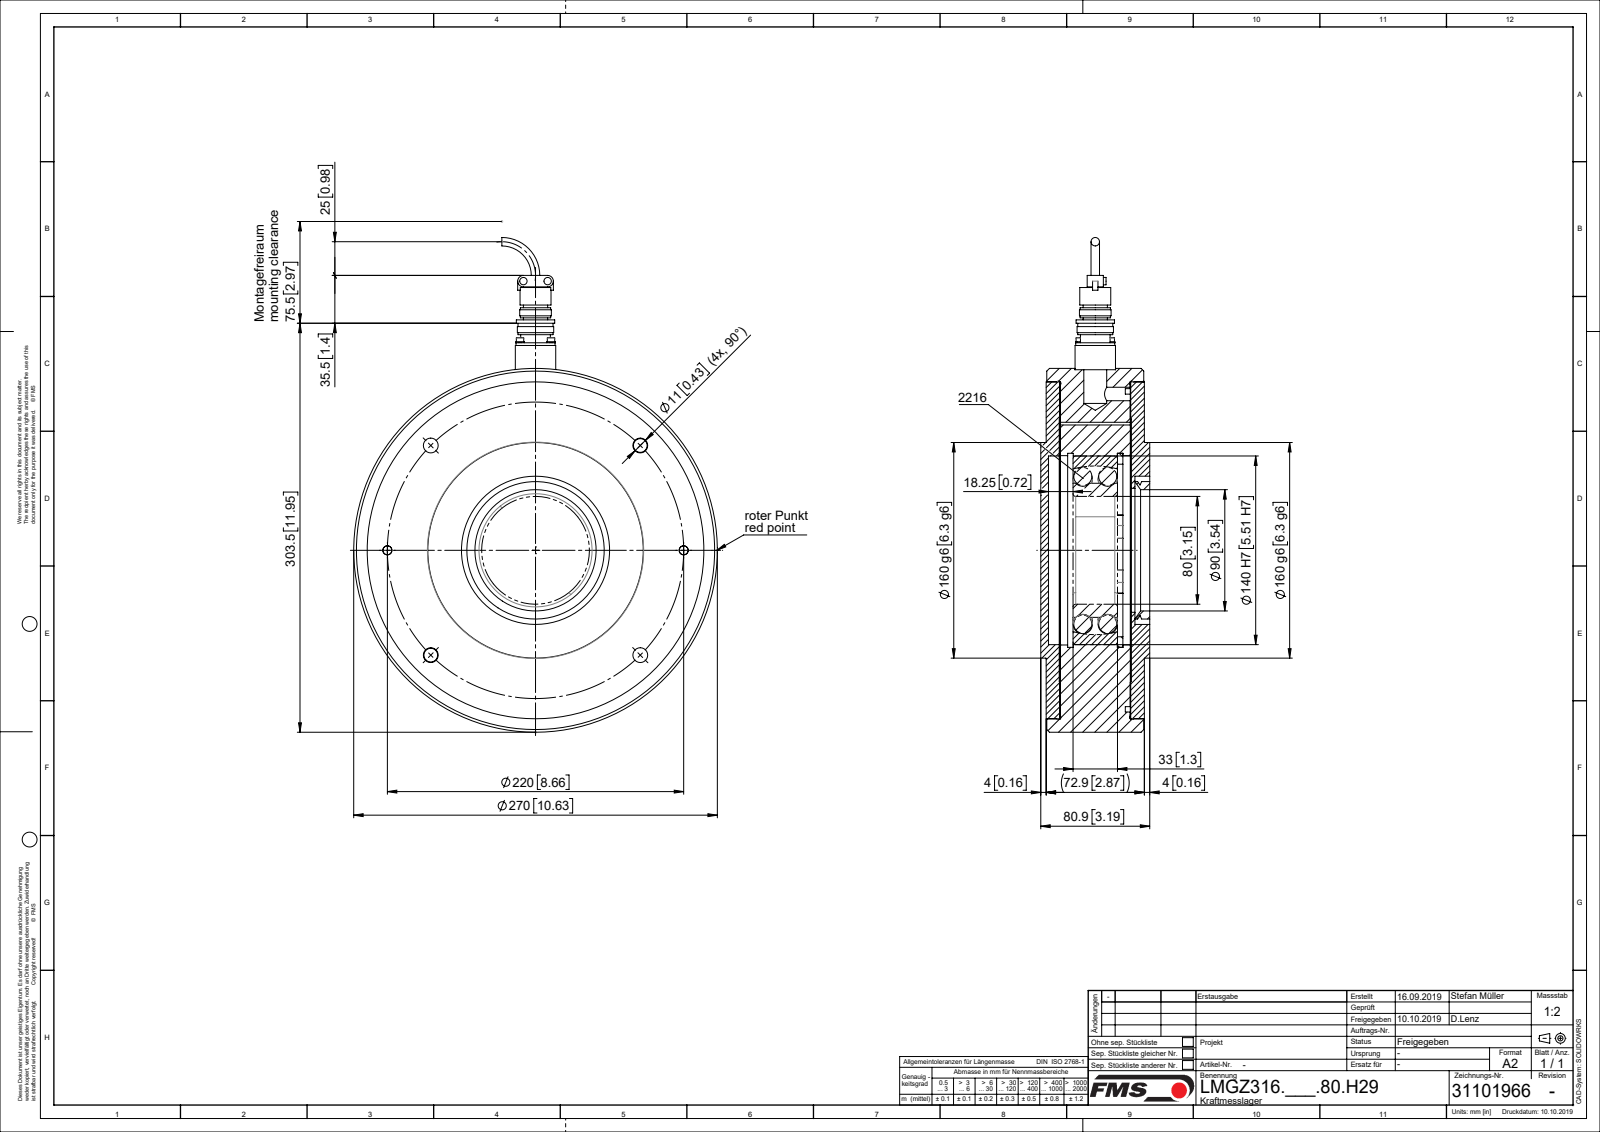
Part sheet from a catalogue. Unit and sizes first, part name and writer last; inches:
Units: inches
Overall size (bounding box): 14.455 × 12.61 × 10.63
Round holes (diameter × count): ⌀0.102 ×4, ⌀0.126 ×4, ⌀0.134 ×4, ⌀0.433 ×4, ⌀0.472 ×4, ⌀0.272 ×2, ⌀0.354 ×2, ⌀0.394 ×2, ⌀0.591 ×2, ⌀0.906 ×1, ⌀3.15 ×1, ⌀3.543 ×1
Round bosses / shafts (diameter × count): ⌀0.217 ×6, ⌀0.244 ×4, ⌀0.118 ×4, ⌀0.098 ×4, ⌀0.512 ×2, ⌀0.315 ×2, ⌀10.63 ×1, ⌀9.843 ×1
Partial cylindrical surfaces — rounded edges, fillets, slot ends (radius × count): R0.167 ×2
Main face-to-face distances: 2.059, 0.406, 2.047, 2.079, 0.02, 2.472, 0.394, 2.453, 0.157, 0.374
Hole centre spacings: 4.331, 0.64, 0.906, 3.315, 6.124, 8.002, 8.661, 1.281
Volume: 219.5 in³ · Surface area: 883.8 in²
Bodies: 20 solids, 380 faces (102 planar, 224 cylindrical, 54 other)
Part name (STEP PRODUCT): L50045; L4899004; TEIL1; L49342 (+8 more)
STEP written by: Mechanical Desktop 2007 (CONFIG_CONTROL_DESIGN)
